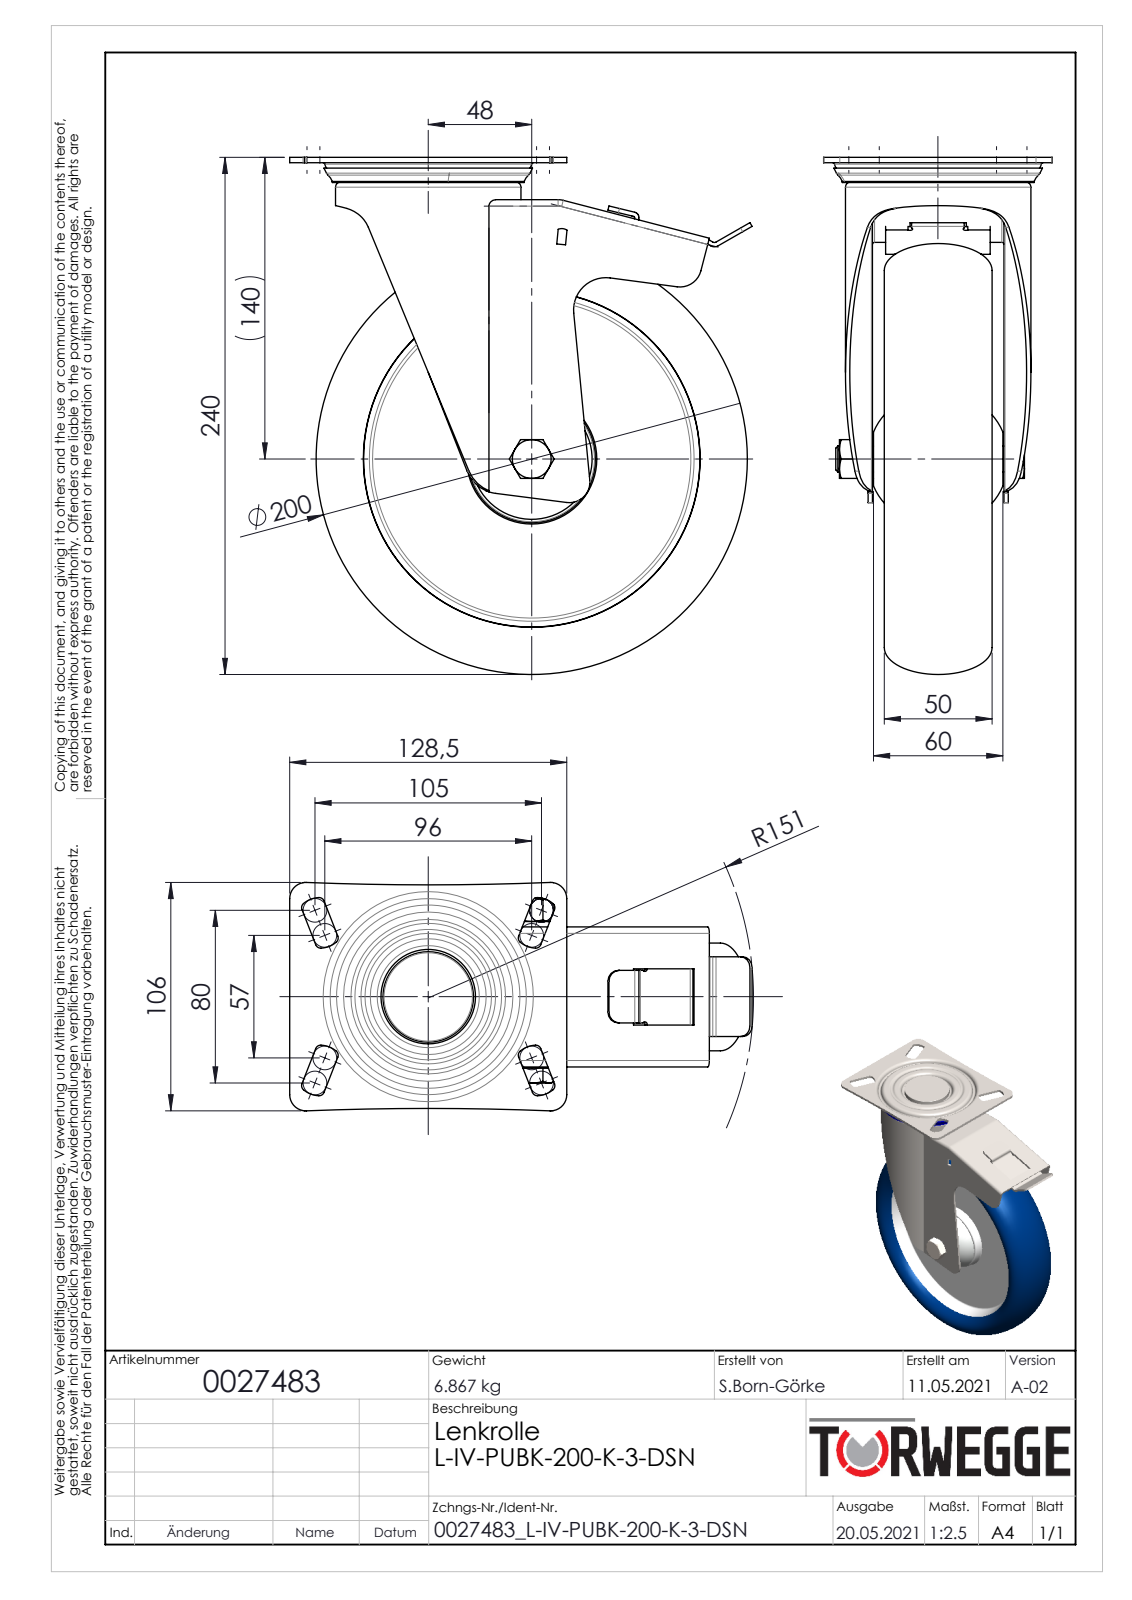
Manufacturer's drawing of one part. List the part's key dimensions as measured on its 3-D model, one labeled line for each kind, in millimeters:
Part name (STEP PRODUCT): 0027483
STEP written by: SolidWorks 2020 (AUTOMOTIVE_DESIGN)
Units: millimetres
Bodies: 12 solids, 529 faces (131 planar, 135 cylindrical, 263 other)
Overall size (bounding box): 240 × 214.44 × 106
Volume: 940 166 mm³ · Surface area: 317 006 mm²
Round holes (diameter × count): ⌀10.2 ×1, ⌀12 ×1, ⌀12.2 ×1, ⌀12.3 ×1, ⌀34 ×1, ⌀38 ×1, ⌀44 ×1, ⌀47 ×1, ⌀50.5 ×1, ⌀54 ×1, ⌀82 ×1
Round bosses / shafts (diameter × count): ⌀89 ×1, ⌀86 ×1, ⌀54.5 ×1, ⌀42 ×1, ⌀41 ×1, ⌀38 ×1, ⌀20.2 ×1, ⌀20 ×1
Partial cylindrical surfaces — rounded edges, fillets, slot ends (radius × count): R2.5 ×17, R1.25 ×5, R7.5 ×5, R1 ×4, R3 ×4, R11.75 ×4, R1.5 ×2, R2 ×2
Main face-to-face distances: 2, 27, 38, 11, 63, 25, 36, 2.5, 65, 61
